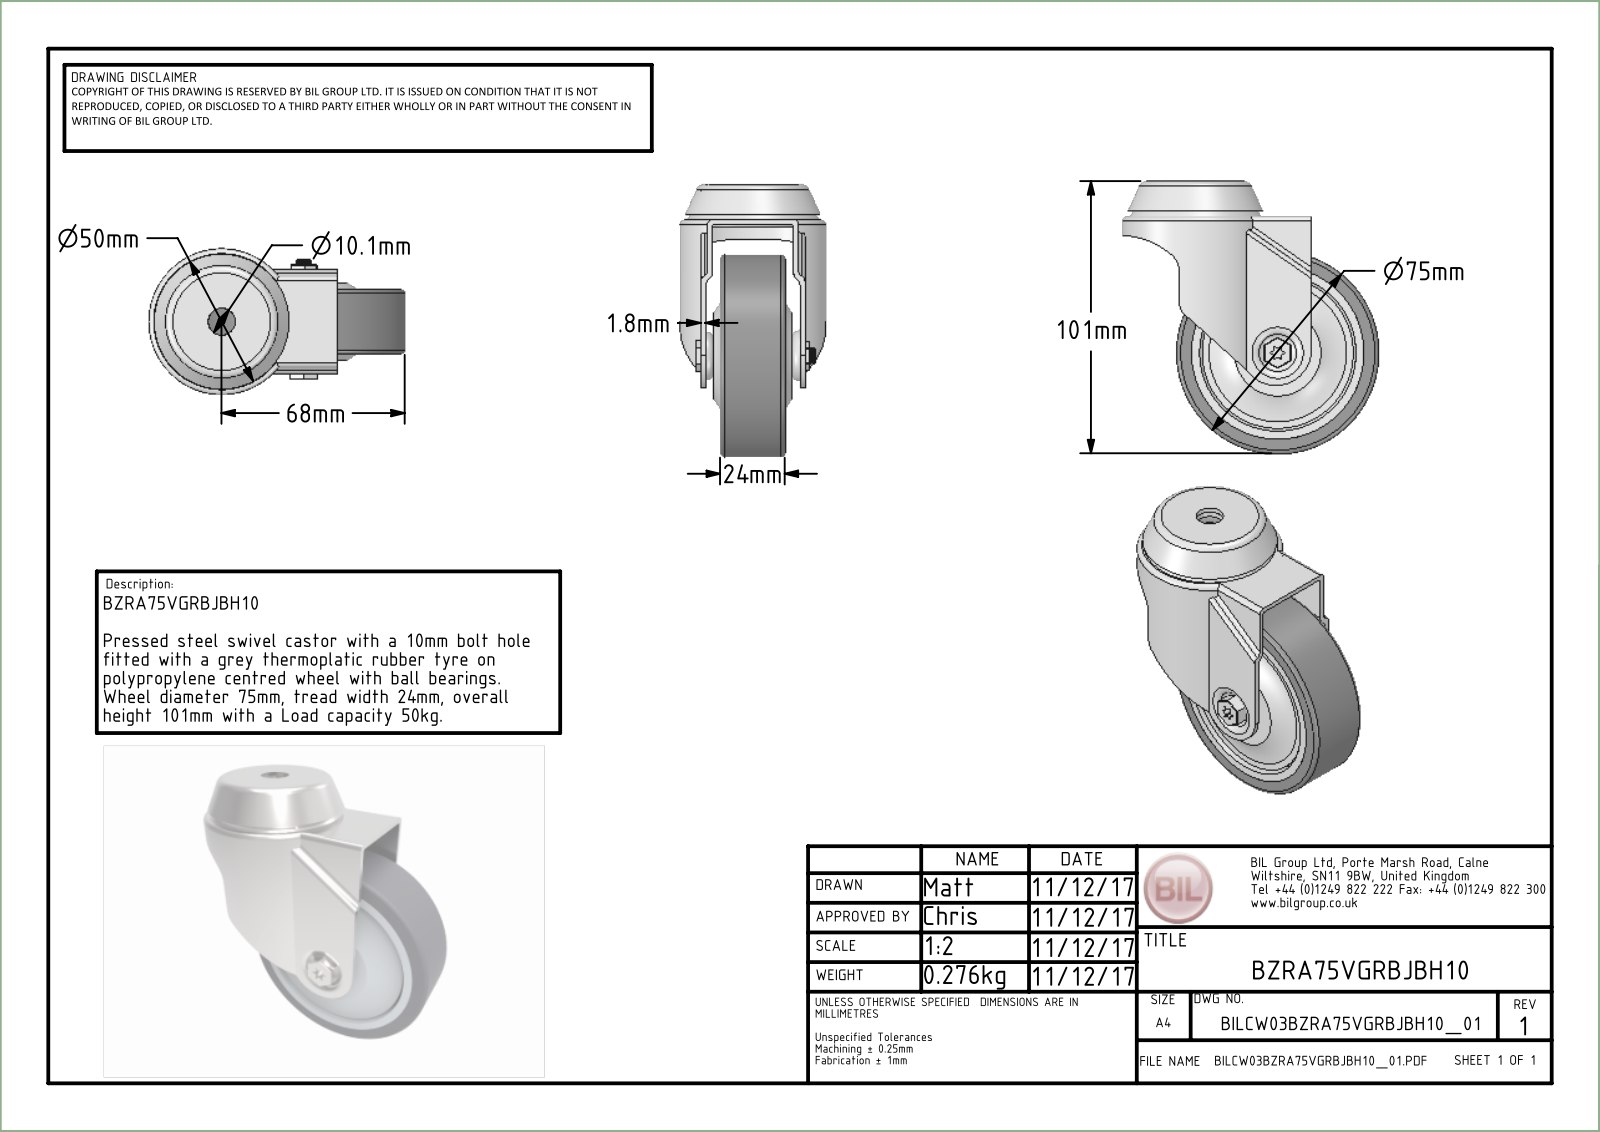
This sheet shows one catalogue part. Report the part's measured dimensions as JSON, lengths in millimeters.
{"part_name": "BZRA75VGRBJBH10 v3; BZRA75ASBH10 v1; ZINC PLATED PRESSED STEEL FORKS; ZINC PLATED PRESSED STEEL HEAD (+7 more)", "step_written_by": "Autodesk Translation Framework v13.20.0.188 (AP242_MANAGED_MODEL_BASED_3D_ENGINEERING_MIM_LF)", "units": "millimeters", "bodies": {"solids": 19, "faces": 403, "planar": 105, "cylindrical": 140, "other": 158}, "overall_size": [101, 90, 50], "volume_mm3": 95942, "surface_area_mm2": 74005, "round_holes": [[6, 1], [6.2, 1], [6.5, 1], [8.5, 1], [10.5, 1], [10.55, 1], [11.2, 1], [12.74, 1], [16, 1], [18, 1], [18.3, 1], [19.2, 1]], "round_bosses_or_shafts": [[56, 1], [30.75, 1], [22, 1], [18.7, 1], [18.32, 1], [14, 1], [11.6, 1], [10, 1]], "partial_cylinders_radius": [[1, 18], [1.8, 14], [0.5, 12], [0.4, 6], [0.9, 6], [2.12, 1], [4.63, 1], [8, 1]], "face_to_face_distances": [10.25, 13.75, 2, 3.5, 6.25, 2.25, 24.25, 3.25, 7.5, 4]}
